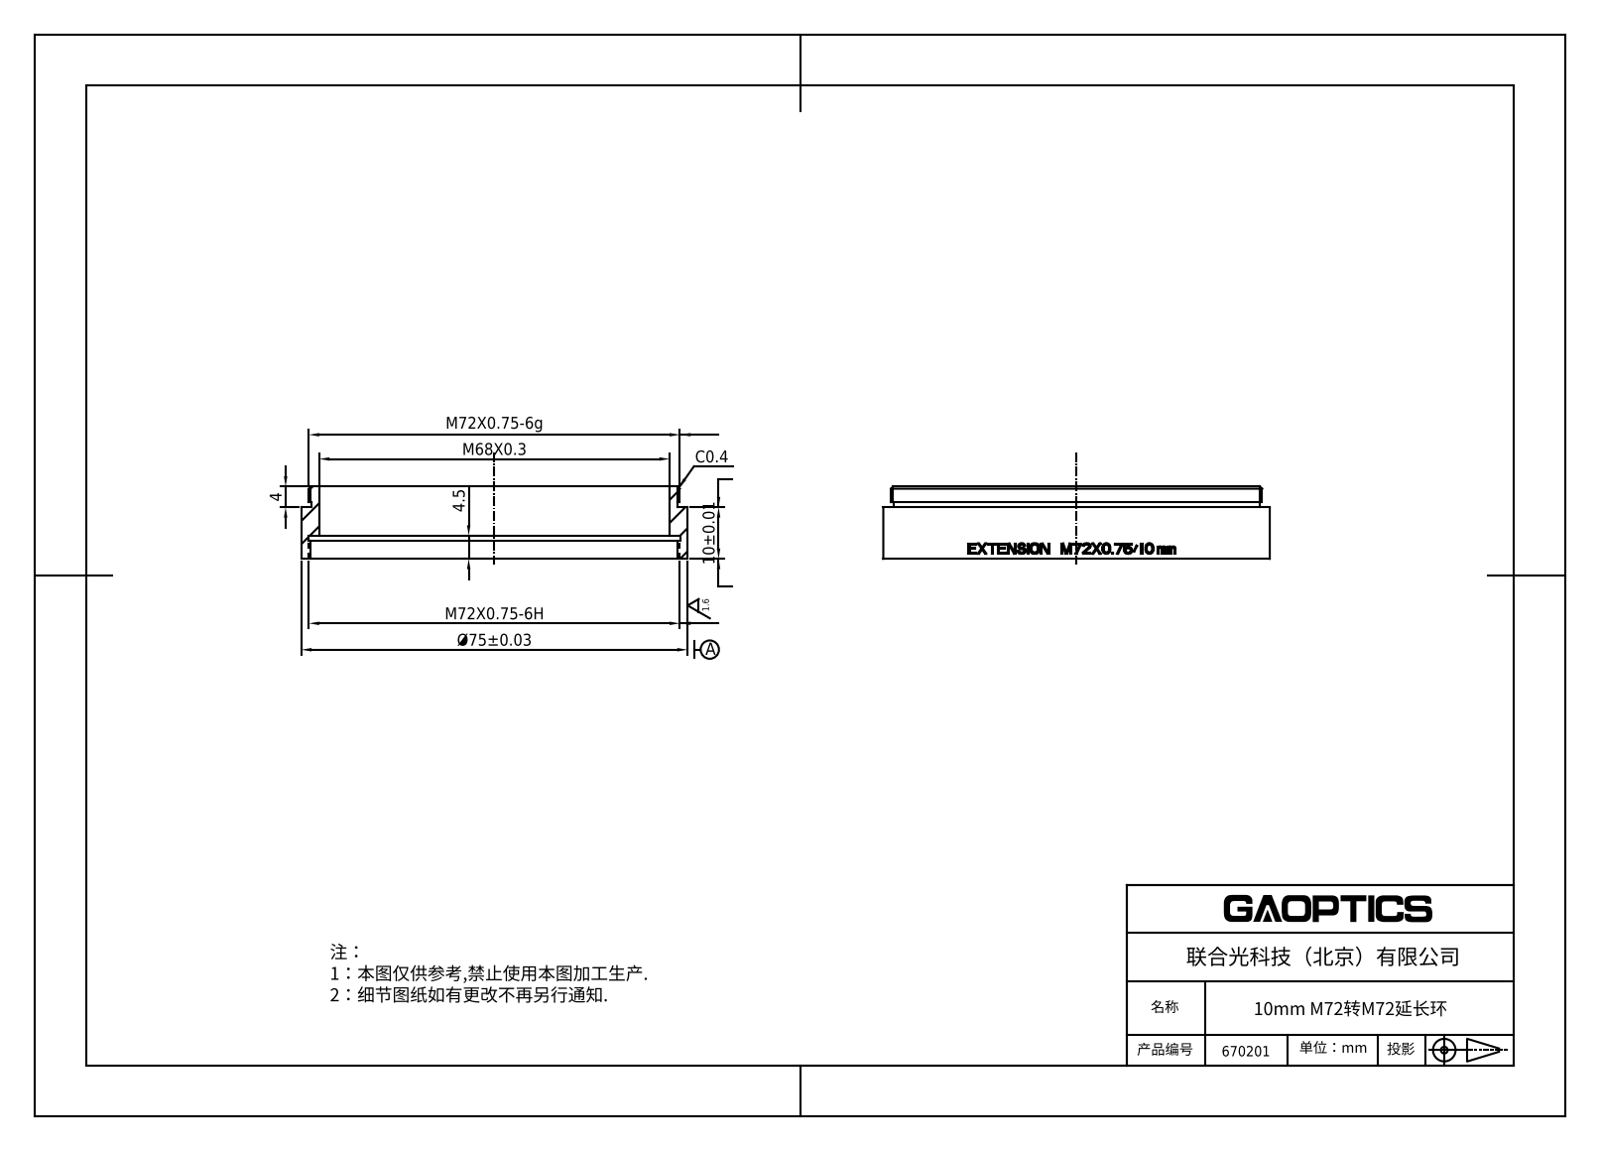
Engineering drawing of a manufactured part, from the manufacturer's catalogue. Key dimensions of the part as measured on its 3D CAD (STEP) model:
Part name (STEP PRODUCT): 10mm
STEP written by: SolidWorks 2019 (CONFIG_CONTROL_DESIGN)
Units: millimetres
Bodies: 1 solid, 57 faces (6 planar, 45 cylindrical, 6 other)
Overall size (bounding box): 75 × 75 × 14
Volume: 7 636 mm³ · Surface area: 8 584 mm²
Round holes (diameter × count): ⌀68 ×1, ⌀71.2 ×1, ⌀72.2 ×1
Round bosses / shafts (diameter × count): ⌀75 ×1, ⌀72 ×1, ⌀71 ×1
Main face-to-face distances: 5.5, 4.5, 10, 14, 9.5, 4, 1, 6.5, 3.5, 10.5
